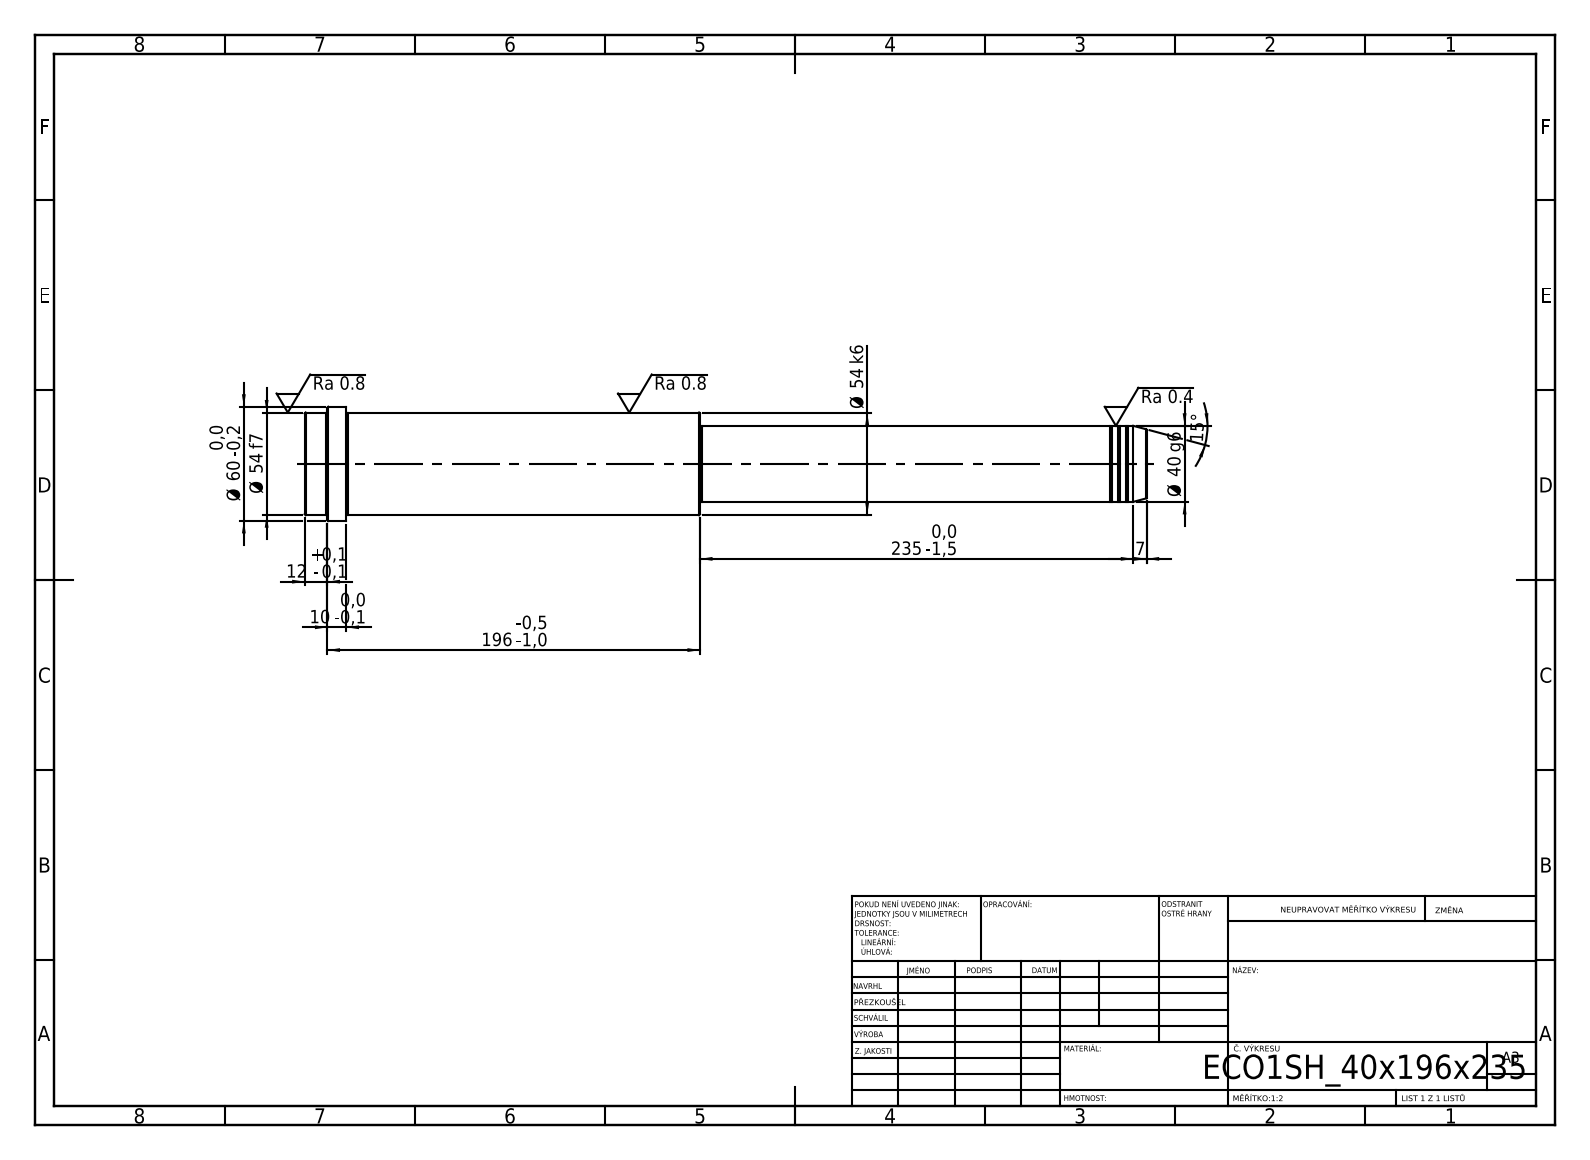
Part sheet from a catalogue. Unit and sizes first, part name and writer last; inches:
Units: inches
Overall size (bounding box): 17.441 × 2.362 × 2.362
Round bosses / shafts (diameter × count): ⌀2.362 ×1, ⌀2.126 ×1, ⌀1.575 ×1, ⌀1.535 ×1
Main face-to-face distances: 8.189, 9.252, 17.441, 16.575, 7.323, 0.866, 16.969, 7.717, 0.394, 0.472
Volume: 47.34 in³ · Surface area: 109.7 in²
Bodies: 1 solid, 52 faces (6 planar, 16 cylindrical, 30 other)
STEP written by: SolidWorks 2019 (CONFIG_CONTROL_DESIGN)
